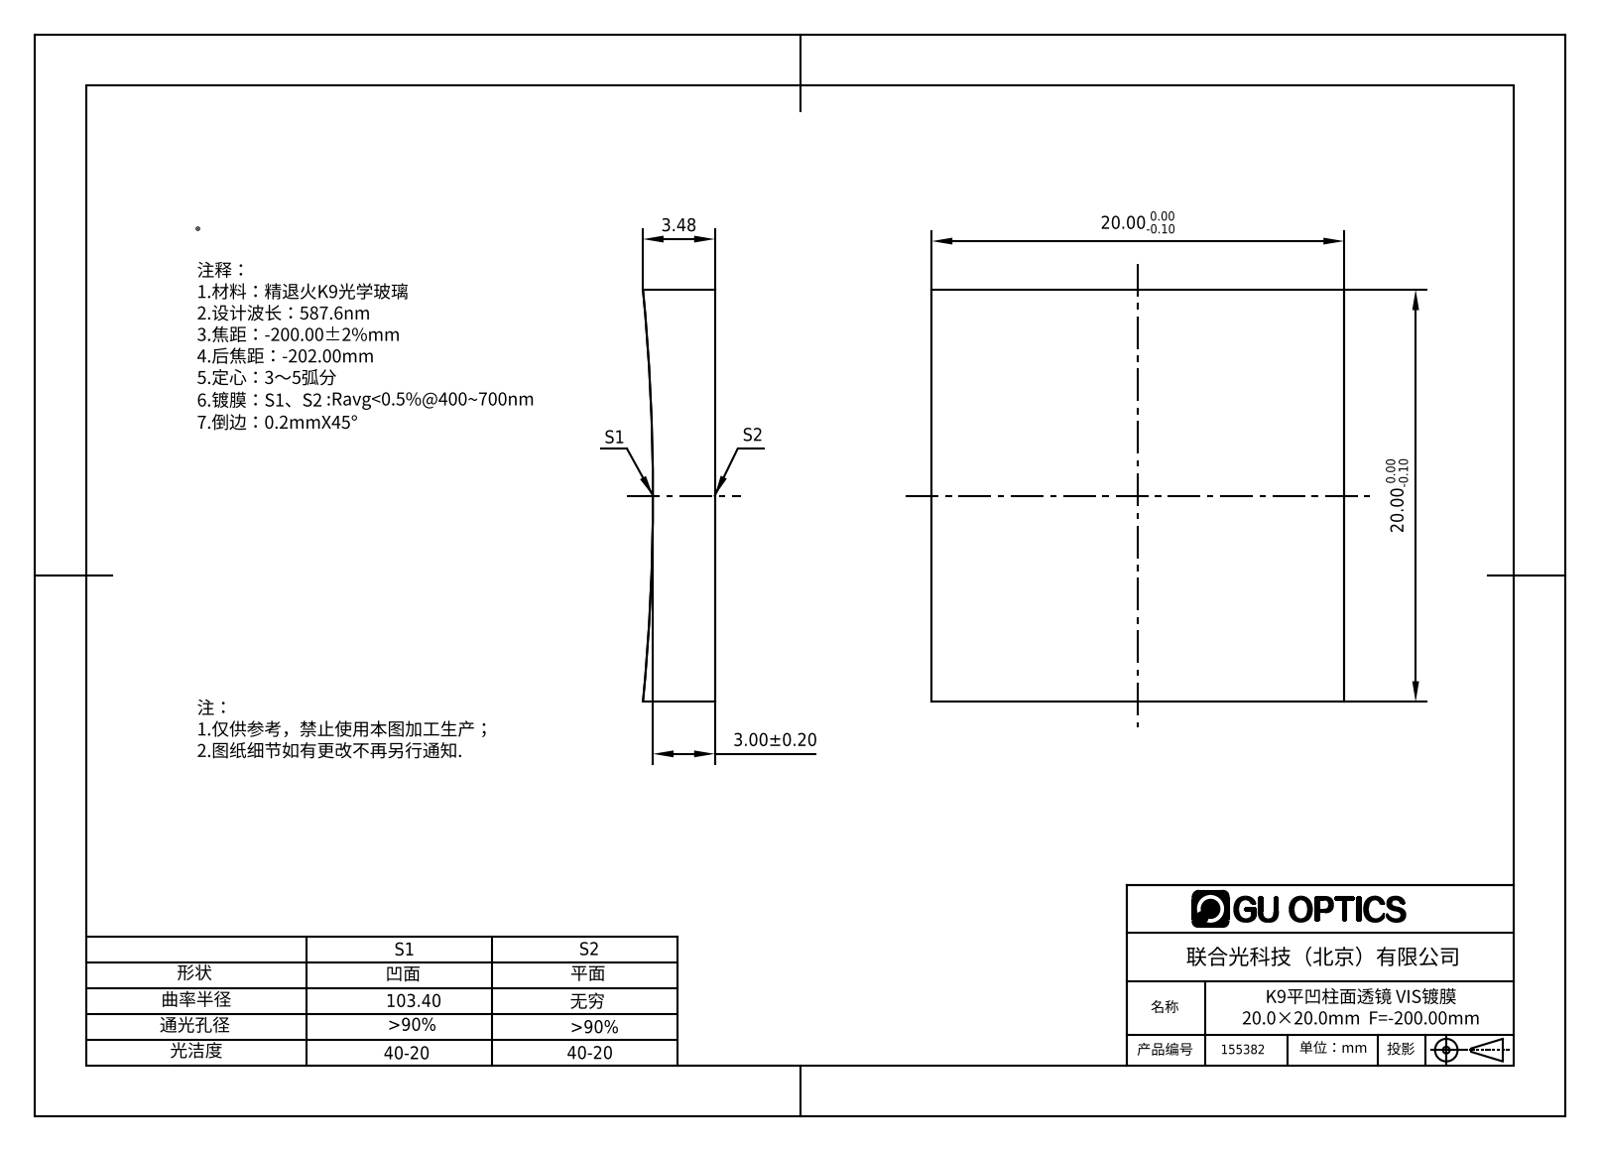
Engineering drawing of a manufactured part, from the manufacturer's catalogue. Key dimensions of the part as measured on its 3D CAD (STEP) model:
Part name (STEP PRODUCT): 155349
STEP written by: SolidWorks 2016 (AUTOMOTIVE_DESIGN)
Units: millimetres
Bodies: 1 solid, 6 faces (5 planar, 1 cylindrical, 0 other)
Overall size (bounding box): 20 × 20 × 3.48
Volume: 1 265 mm³ · Surface area: 1 066 mm²
Partial cylindrical surfaces — rounded edges, fillets, slot ends (radius × count): R103.4 ×1
Main face-to-face distances: 20
